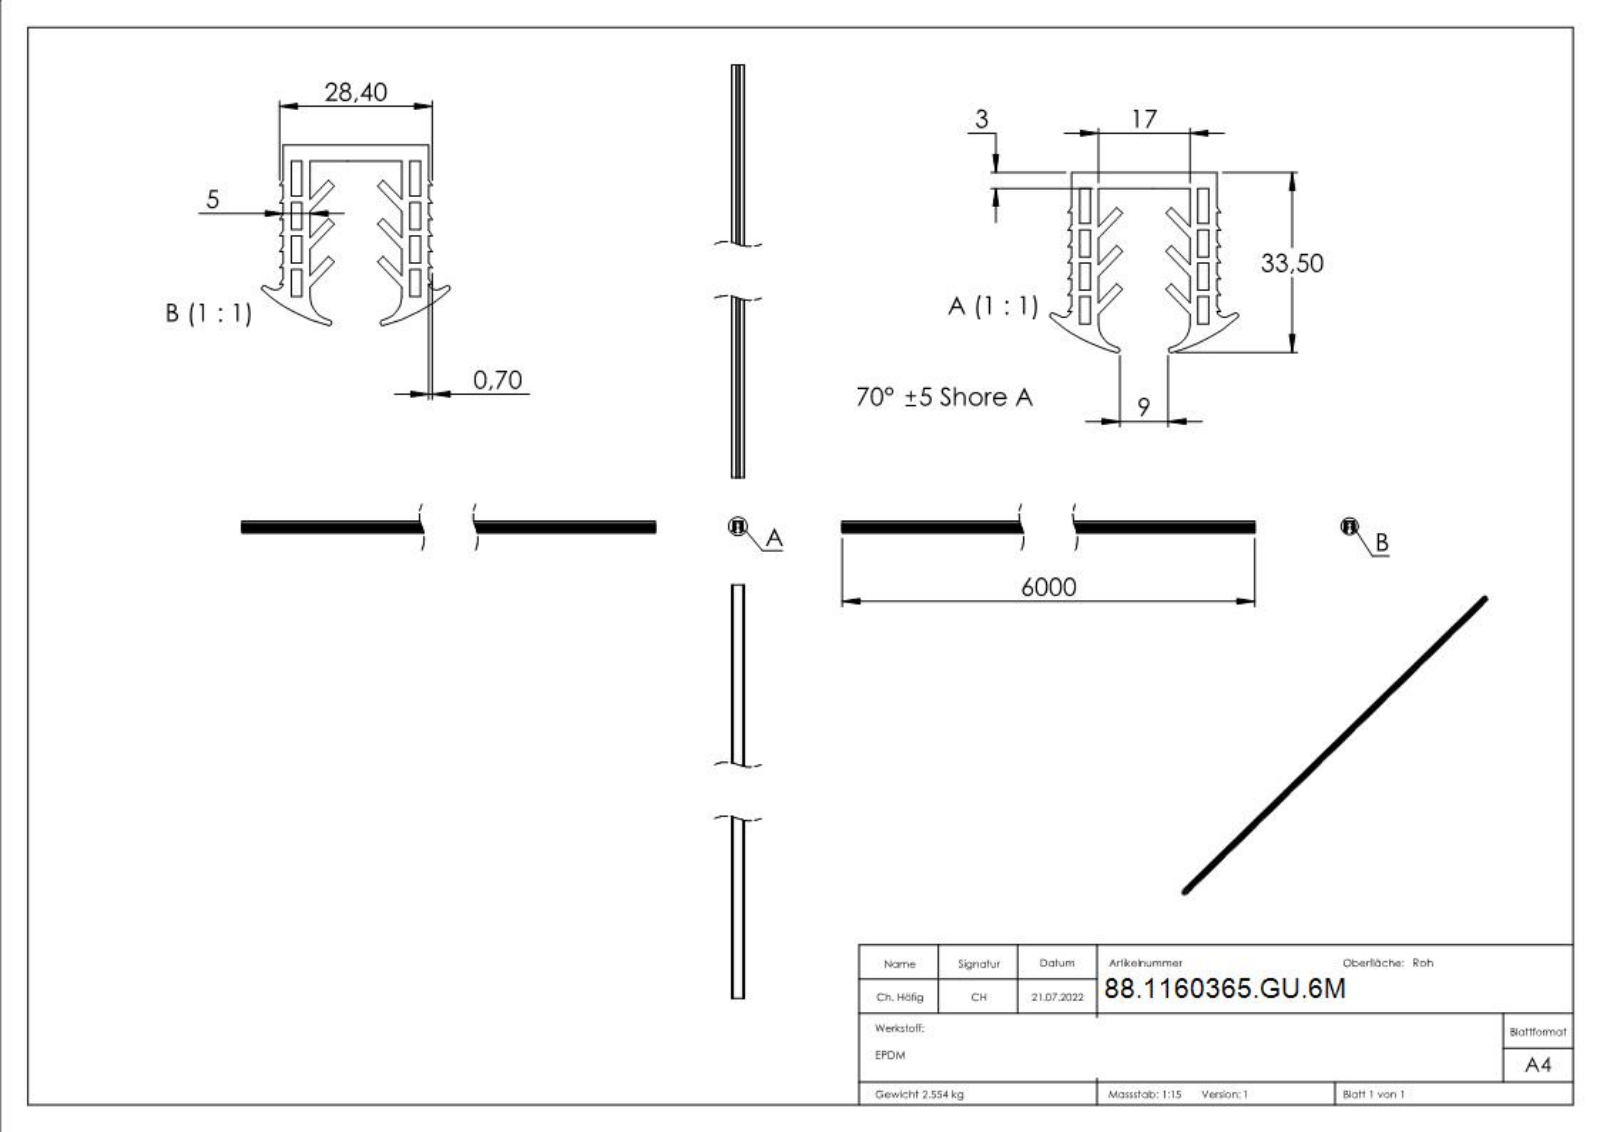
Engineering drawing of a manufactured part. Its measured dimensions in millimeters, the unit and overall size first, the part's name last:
Units: millimetres
Overall size (bounding box): 6000 × 35 × 33.5
Partial cylindrical surfaces — rounded edges, fillets, slot ends (radius × count): R0.5 ×4, R1.5 ×2, R4.5 ×2, R30 ×2
Main face-to-face distances: 1.5, 22, 3.5, 5, 2, 23.5, 25.5, 20.5, 18.5, 3
Volume: 2 163 000 mm³ · Surface area: 2 373 000 mm²
Bodies: 1 solid, 408 faces (256 planar, 10 cylindrical, 142 other)
Part name (STEP PRODUCT): 60365-GU-6M
STEP written by: SolidWorks 2018 (CONFIG_CONTROL_DESIGN)
